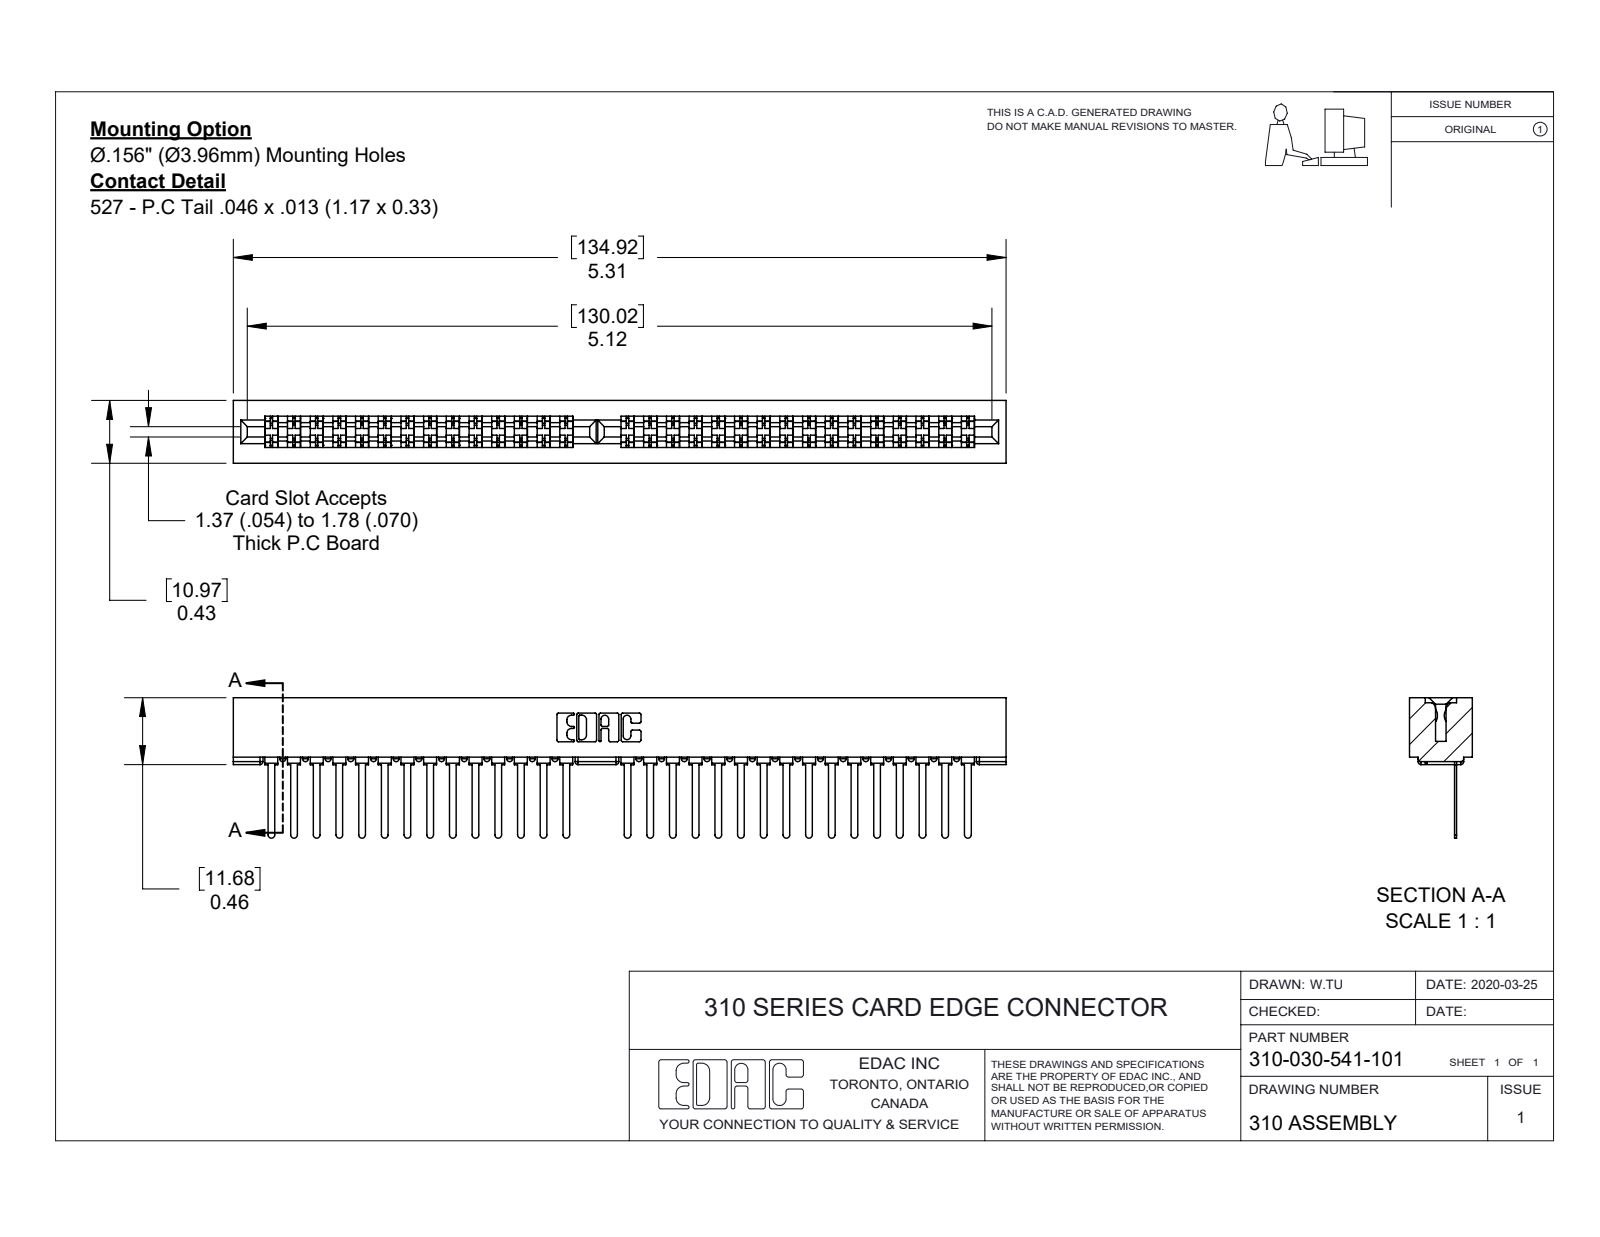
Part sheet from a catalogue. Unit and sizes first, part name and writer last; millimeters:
Units: millimetres
Overall size (bounding box): 134.93 × 24.54 × 10.97
Partial cylindrical surfaces — rounded edges, fillets, slot ends (radius × count): R0.51 ×98, R0.58 ×30, R0.25 ×22, R0.17 ×6, R0.8 ×6, R0.67 ×3, R0.31 ×2, R0.64 ×2
Main face-to-face distances: 2.76, 8.22, 0.33, 3.09, 7.89, 5.13, 5.46, 10.98, 1.24, 3.89
Volume: 12 186 mm³ · Surface area: 18 059 mm²
Bodies: 31 solids, 2378 faces (1430 planar, 884 cylindrical, 64 other)
Part name (STEP PRODUCT): 307-290-002_541; 310 Part_No Mounting Lugs; 310-030-541-101
STEP written by: SolidWorks 2016 (CONFIG_CONTROL_DESIGN)
